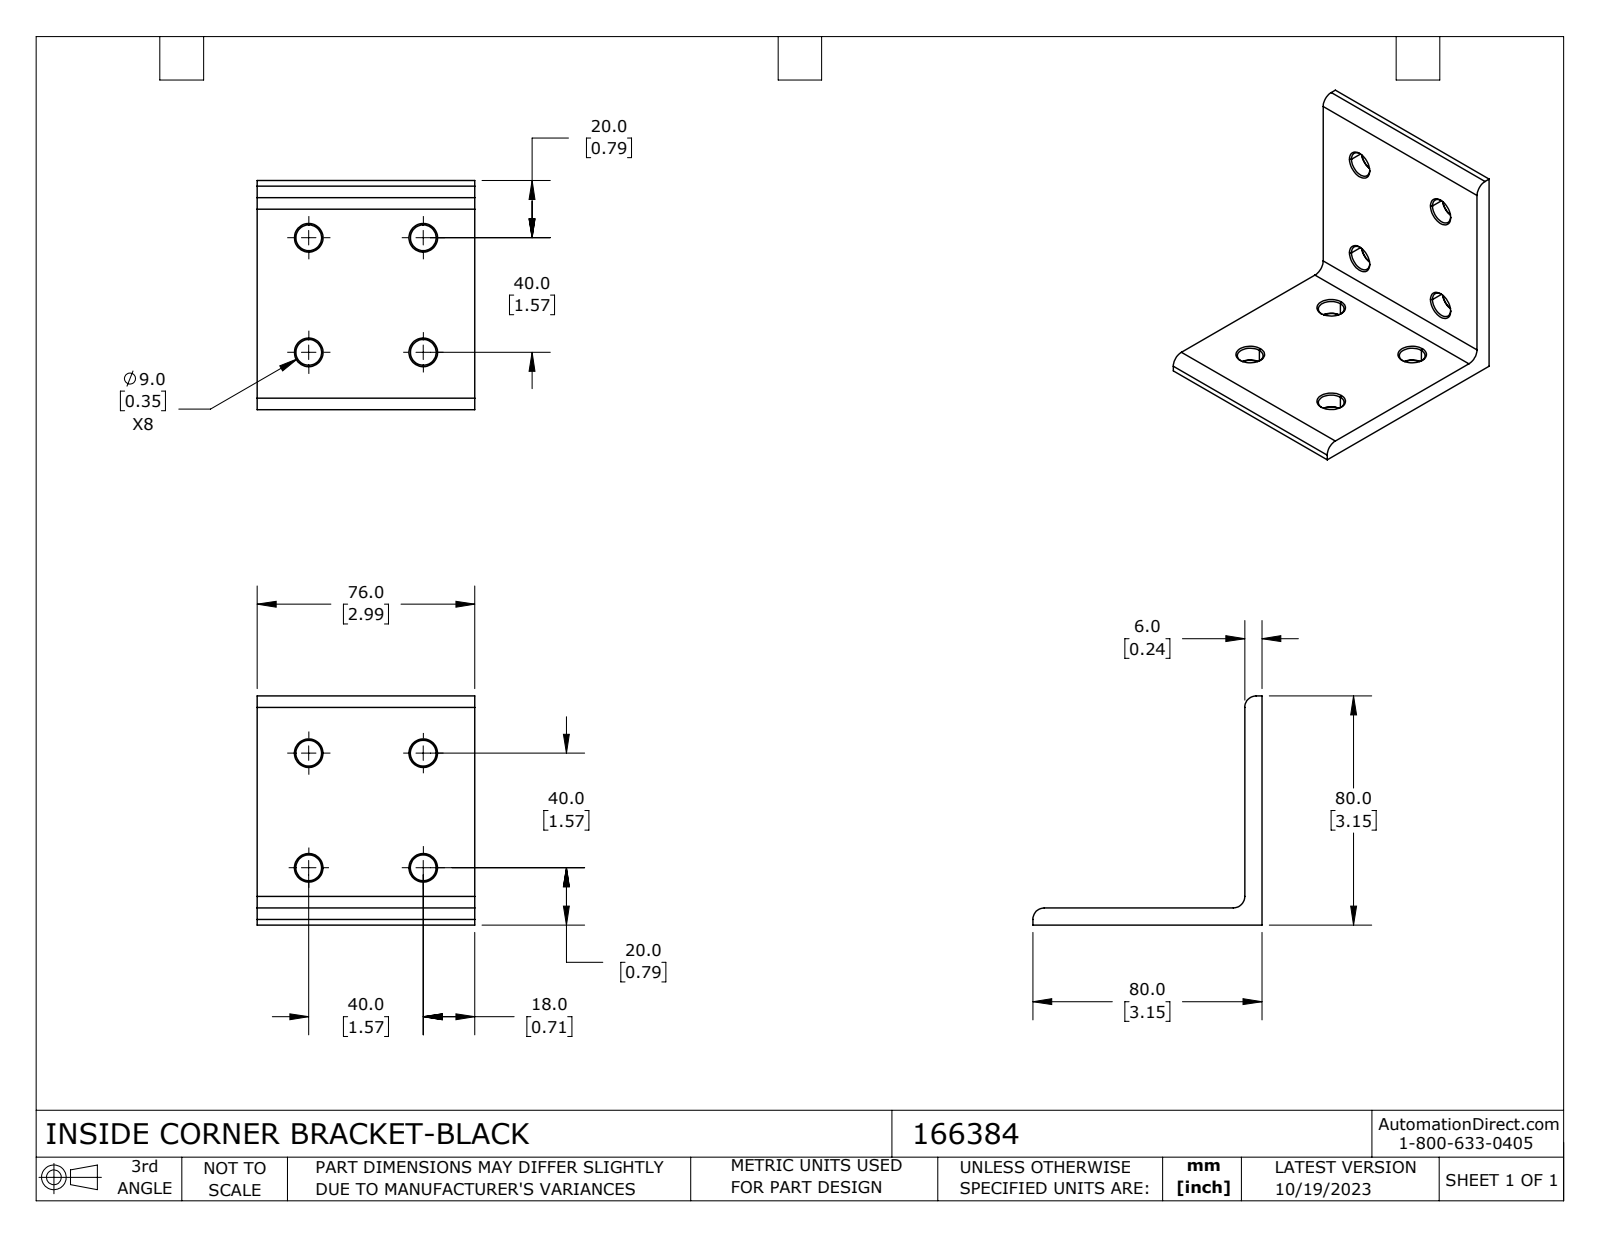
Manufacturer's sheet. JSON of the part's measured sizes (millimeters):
{"part_name": "166384", "step_written_by": "SolidWorks 2023 (CONFIG_CONTROL_DESIGN)", "units": "millimeters", "bodies": {"solids": 1, "faces": 59, "planar": 8, "cylindrical": 19, "other": 32}, "overall_size": [80, 80, 76], "volume_mm3": 66851, "surface_area_mm2": 25982, "round_holes": [[9, 8]], "partial_cylinders_radius": [[4, 3]], "face_to_face_distances": [6, 76, 80, 74], "hole_center_spacings": [40, 56.57]}
